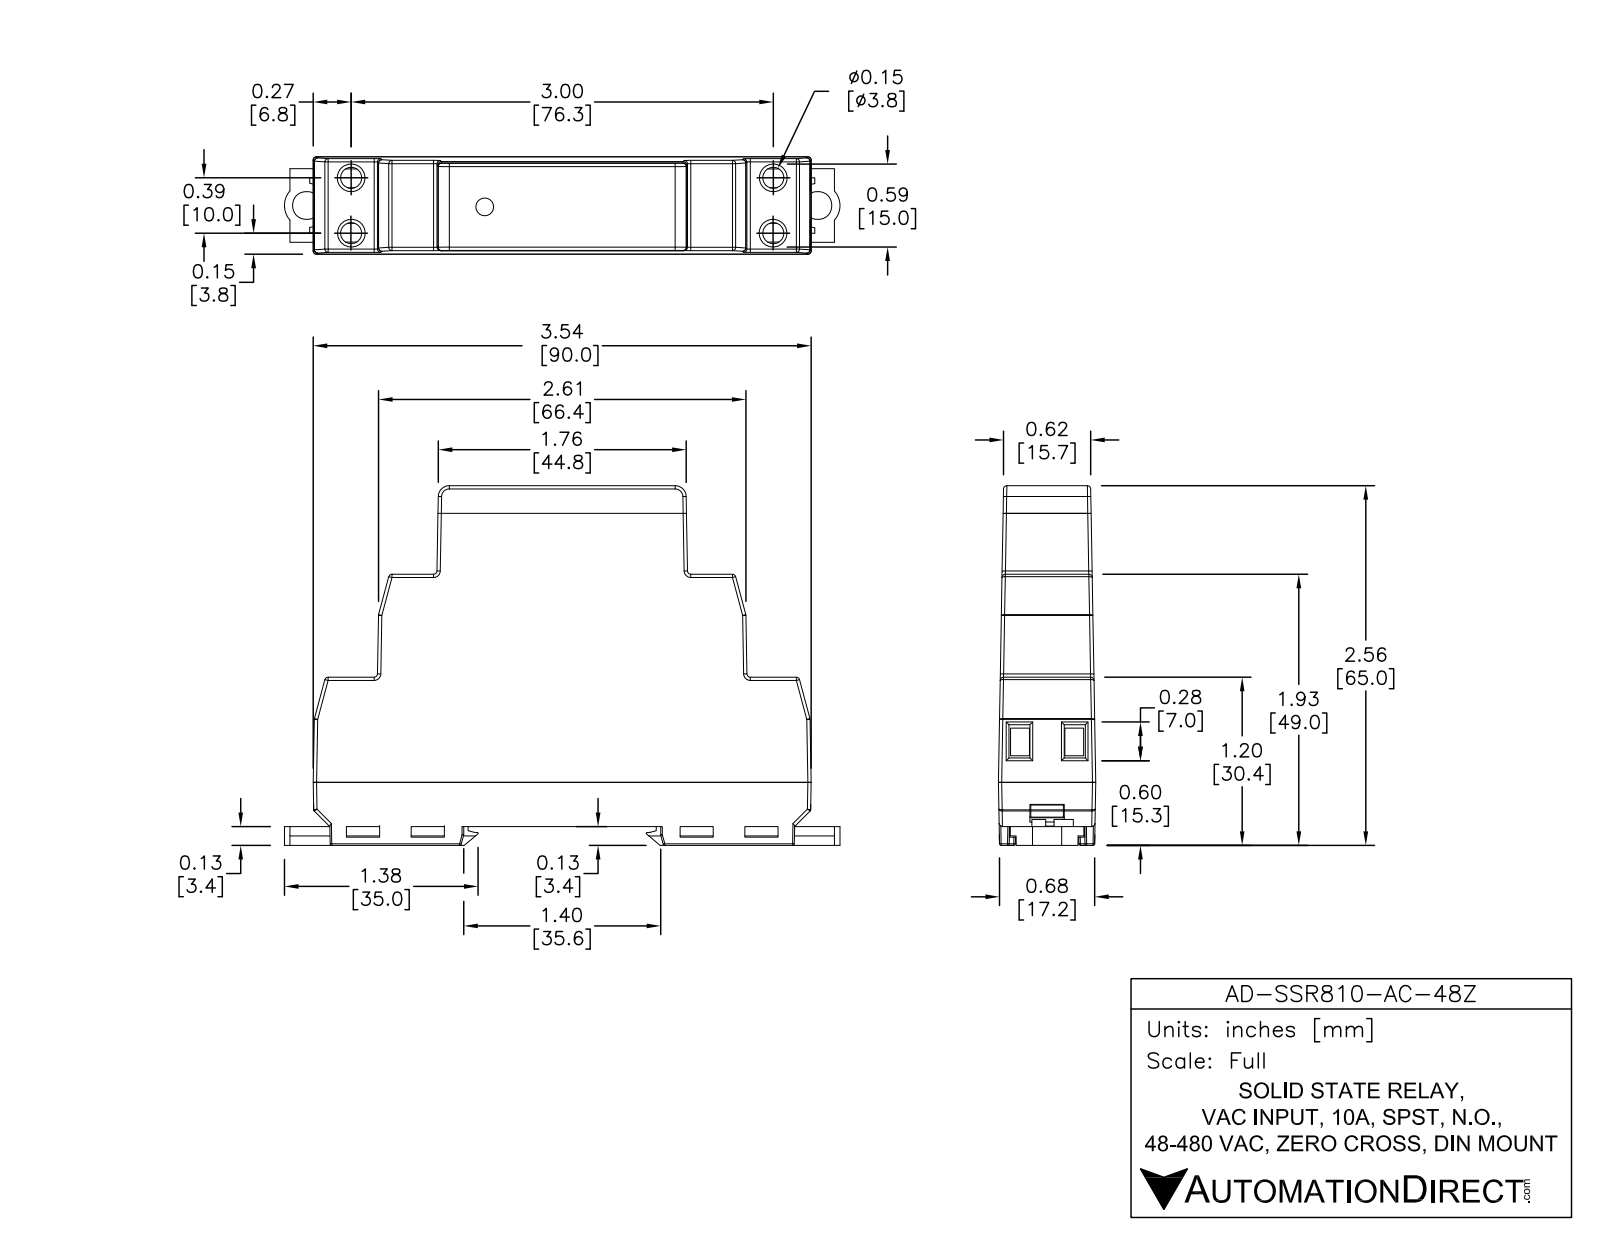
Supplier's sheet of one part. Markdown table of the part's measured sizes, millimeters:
| quantity | value |
| --- | --- |
| part name | AD-SSR810-AC-48Z |
| STEP written by | SolidWorks 2013 (AUTOMOTIVE_DESIGN) |
| units | millimeters |
| bodies | 1 solid, 837 faces (505 planar, 78 cylindrical, 254 other) |
| overall size | 99.7 × 66.4 × 17.4 |
| volume | 75 460 mm³ |
| surface area | 15 630 mm² |
| round holes (diameter × count) | 4.8 × 4, 5.1 × 2 |
| round bosses / shafts (diameter × count) | 2.7 × 1 |
| partial cylindrical surfaces (radius × count) | 0.4 × 41, 1.5 × 2, 4.4 × 2 |
| main face-to-face distances | 64.1, 1.2, 65.4, 10.8, 56.3, 0.6, 1.3, 49.1, 47.9, 16.3 |
| hole center spacings | 8.6, 83.8, 9.2, 76.5, 77, 90.9 |
